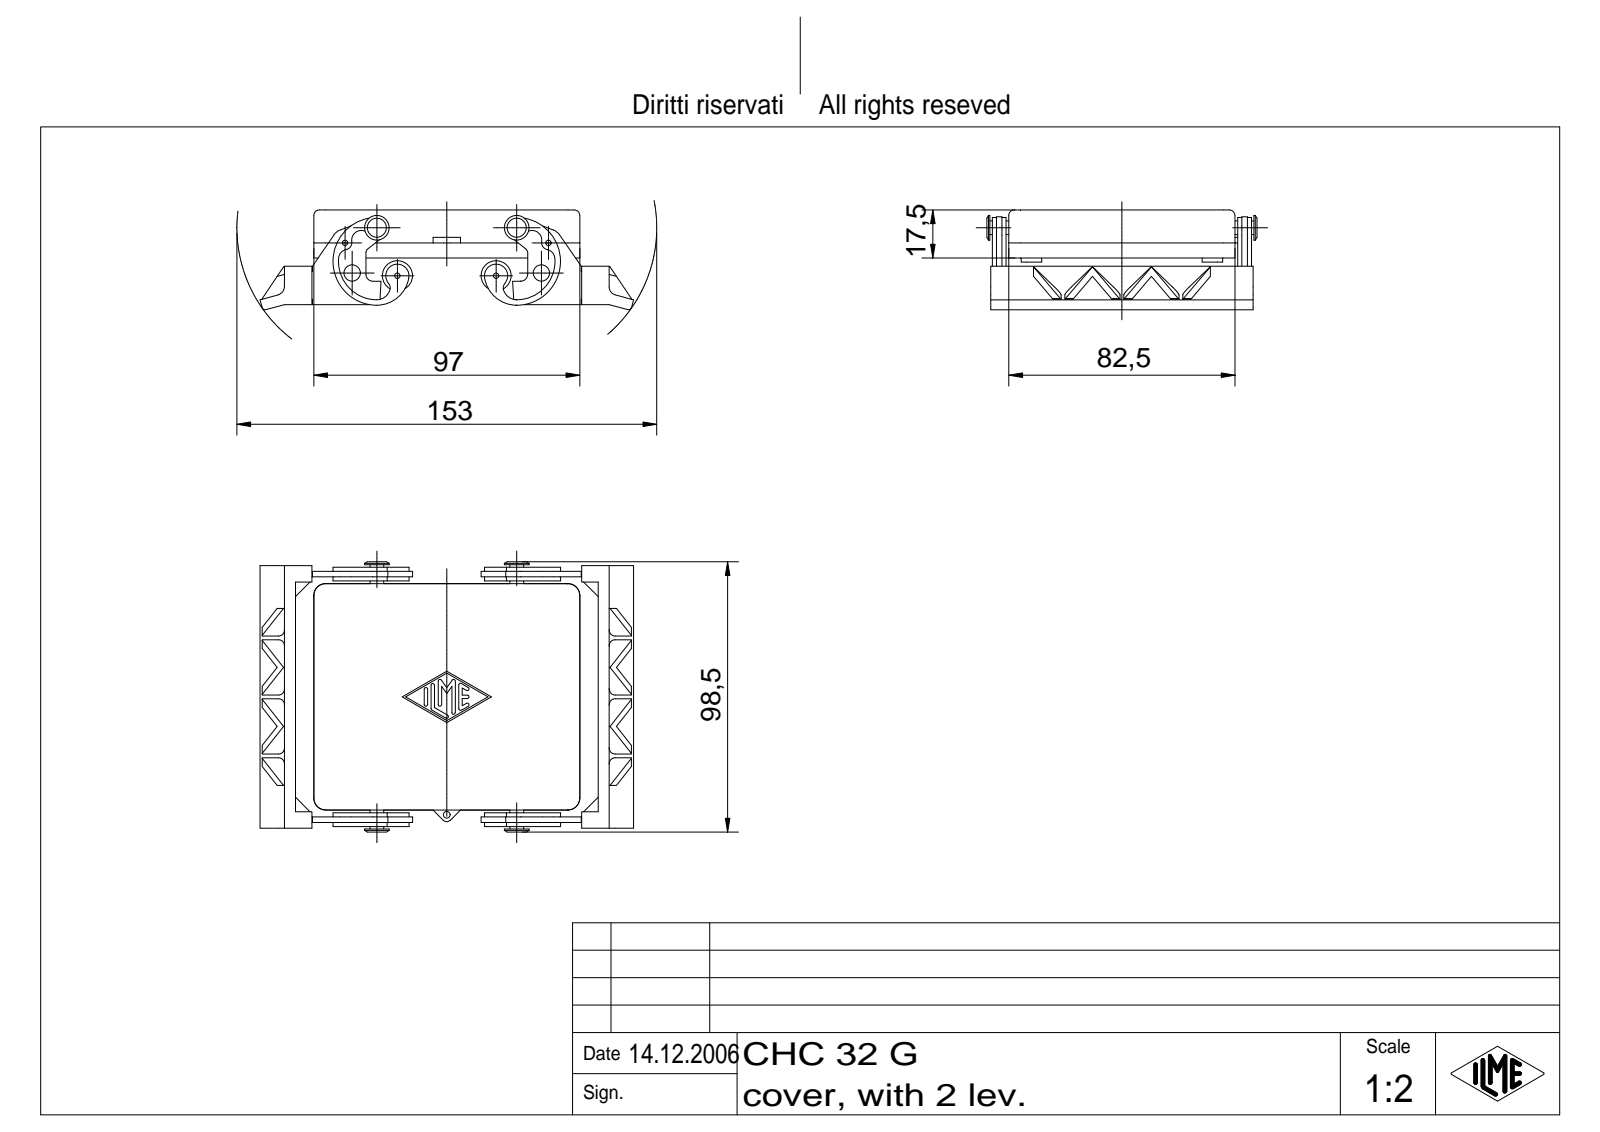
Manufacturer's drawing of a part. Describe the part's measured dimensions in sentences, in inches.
The part is named "CHC 32 G". Its 3-D file was written by "Autodesk Inventor 7 (AUTOMOTIVE_DESIGN)". It is 1 solid with 573 faces: 177 planar, 175 cylindrical and 221 other. Overall it measures 5.364 by 3.878 by 1.433 inches. Its volume is 4.674 cubic inches and its surface area 76.36 square inches. Round holes: 4 of diameter 0.079, 3 of diameter 0.098, 1 of diameter 0.236. Round bosses or shafts: 2 of diameter 0.433, 2 of diameter 0.354, 2 of diameter 0.197. Partial cylindrical surfaces (rounded edges, fillets, slot ends): 14 of radius 0.024, 8 of radius 0.079, 8 of radius 0.169, 6 of radius 0.098, 4 of radius 0.138, 4 of radius 0.197, 2 of radius 0.039, 2 of radius 0.059. The main face-to-face distances are 0.118, 0.177, 3.071, 0.689, 3.248, 0.571, 3.524, 0.079, 0.098, 0.276. The hole center spacings are 0.888, 2.22, 0.445, 0.651, 1.417, 2.067, 2.852, 2.921.
